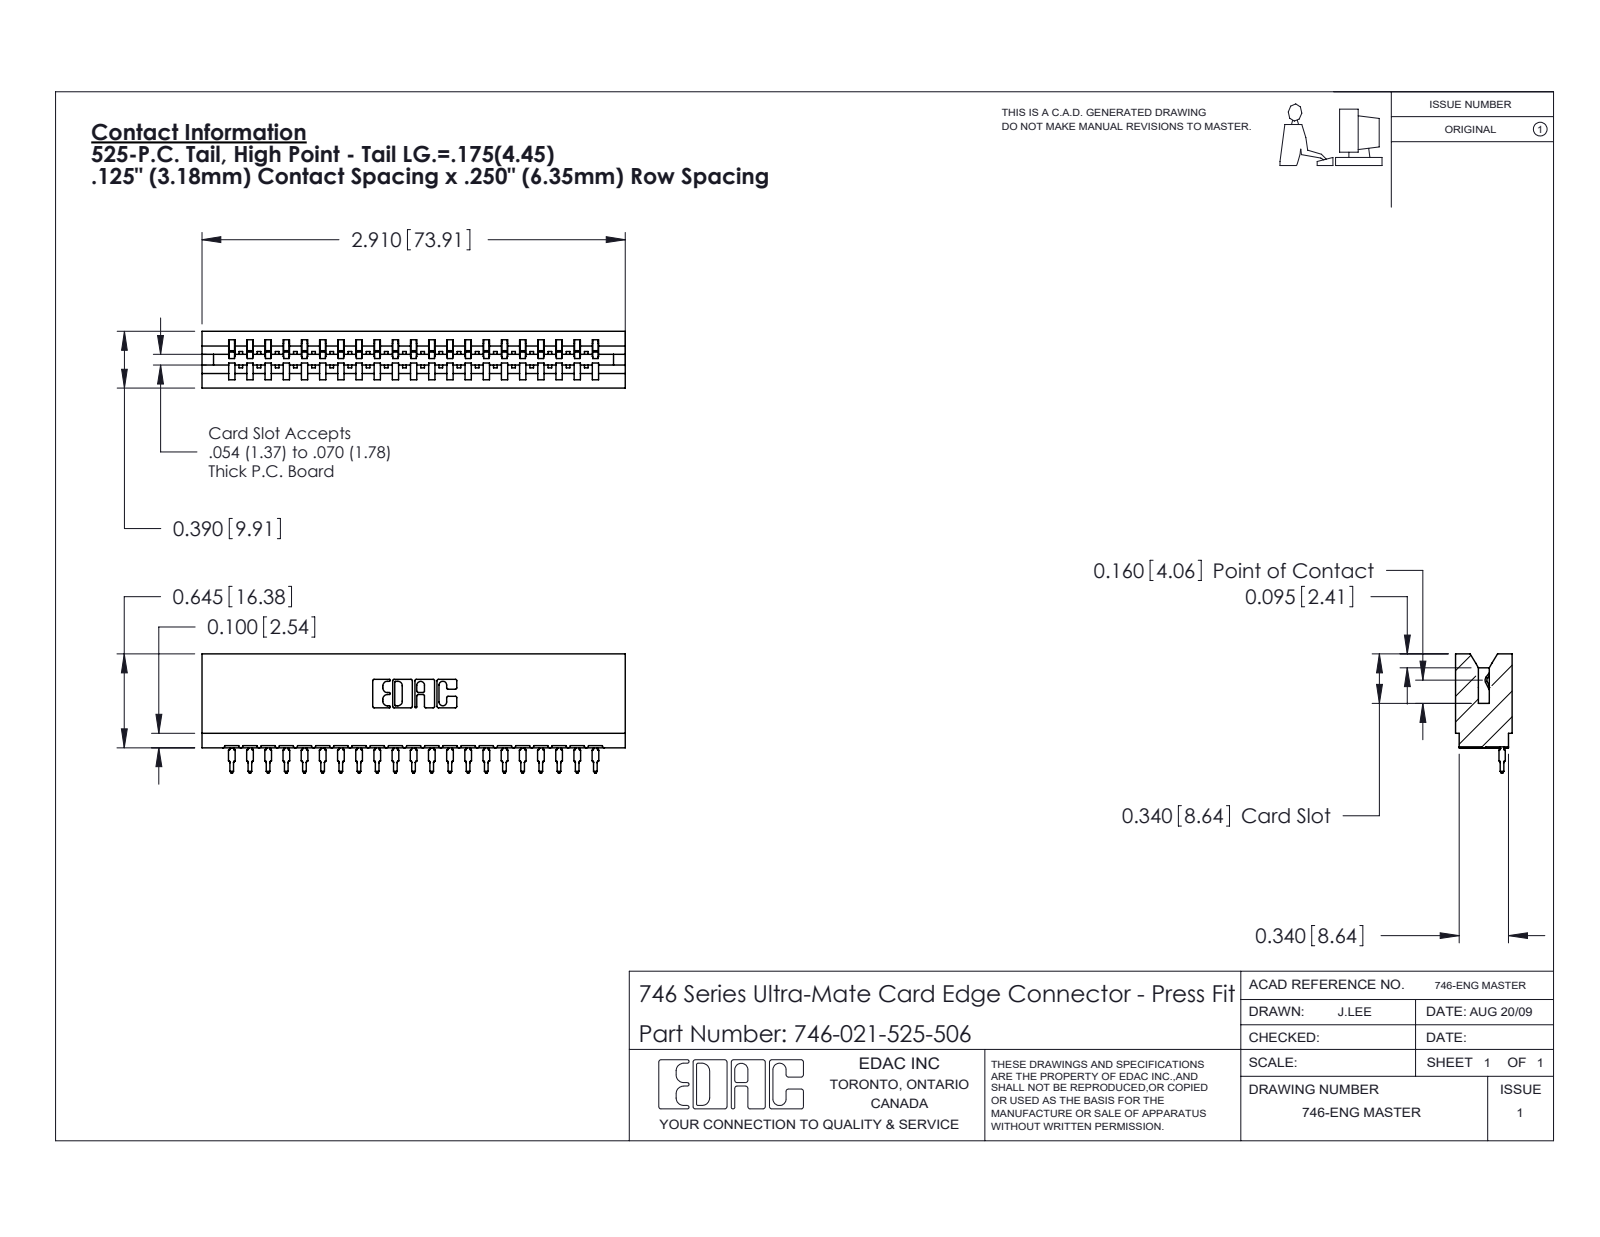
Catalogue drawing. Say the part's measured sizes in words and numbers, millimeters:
The part is named "746-021-525-506; 746-292-001_525; 746 Part_.340 Slot Depth - 06". Its 3-D file was written by "SolidWorks 2020 (CONFIG_CONTROL_DESIGN)". It is 22 solids with 2366 faces: 1379 planar, 441 cylindrical and 546 other. Overall it measures 73.9 by 20.8 by 9.9 millimeters. Its volume is 8 370 cubic millimeters and its surface area 10 880 square millimeters. Partial cylindrical surfaces (rounded edges, fillets, slot ends): 42 of radius 0.5, 22 of radius 0.3, 22 of radius 0.4, 6 of radius 0.2, 6 of radius 0.8, 4 of radius 0.1, 4 of radius 0.3, 3 of radius 0.7. The main face-to-face distances are 8.5, 6.4, 1.4, 9.9, 12.7, 0.6, 1.1, 3.2, 19.1, 3.2.
